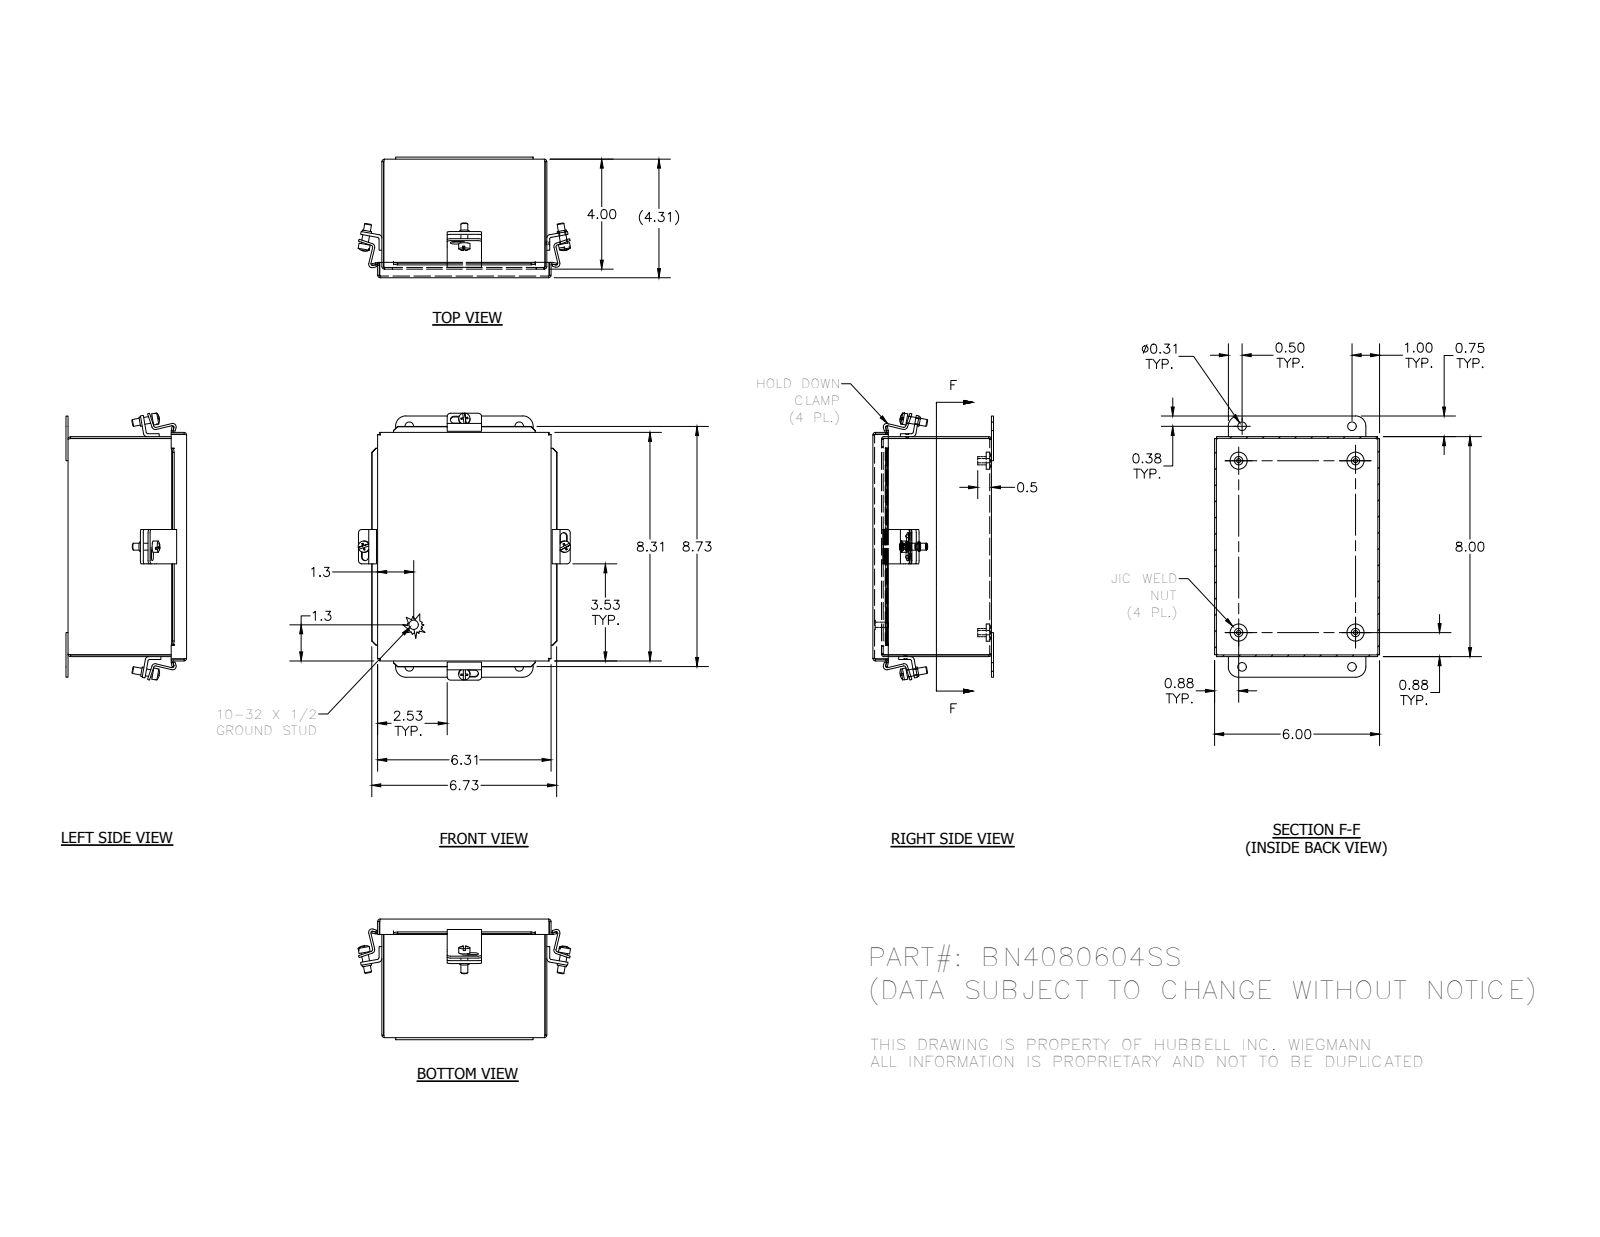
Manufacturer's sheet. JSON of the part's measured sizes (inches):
{"part_name": "BN40806SSLID_1; 372135_1; 34853_1; BN4080604SS (+5 more)", "step_written_by": "SolidWorks 2014 (AUTOMOTIVE_DESIGN)", "units": "inches", "bodies": {"solids": 21, "faces": 589, "planar": 287, "cylindrical": 200, "other": 102}, "overall_size": [9.712, 7.724, 4.388], "volume_in3": 17.41, "surface_area_in2": 547.5, "round_holes": [[0.11, 6], [0.156, 4], [0.196, 4], [0.31, 4]], "round_bosses_or_shafts": [[0.625, 4], [0.41, 4], [0.344, 4], [0.3, 4], [0.25, 4], [0.337, 1], [0.19, 1]], "partial_cylinders_radius": [[0.031, 16], [0.094, 16], [0.125, 16], [0.063, 12], [0.126, 12], [0.133, 8], [0.375, 4]], "face_to_face_distances": [0.063, 4.25, 5.937, 4.313, 4.187, 7.937, 6, 5.875, 8, 7.875], "hole_center_spacings": [1.256, 4.31, 7.501, 8.559, 0.75, 0.063, 0.753, 4]}
